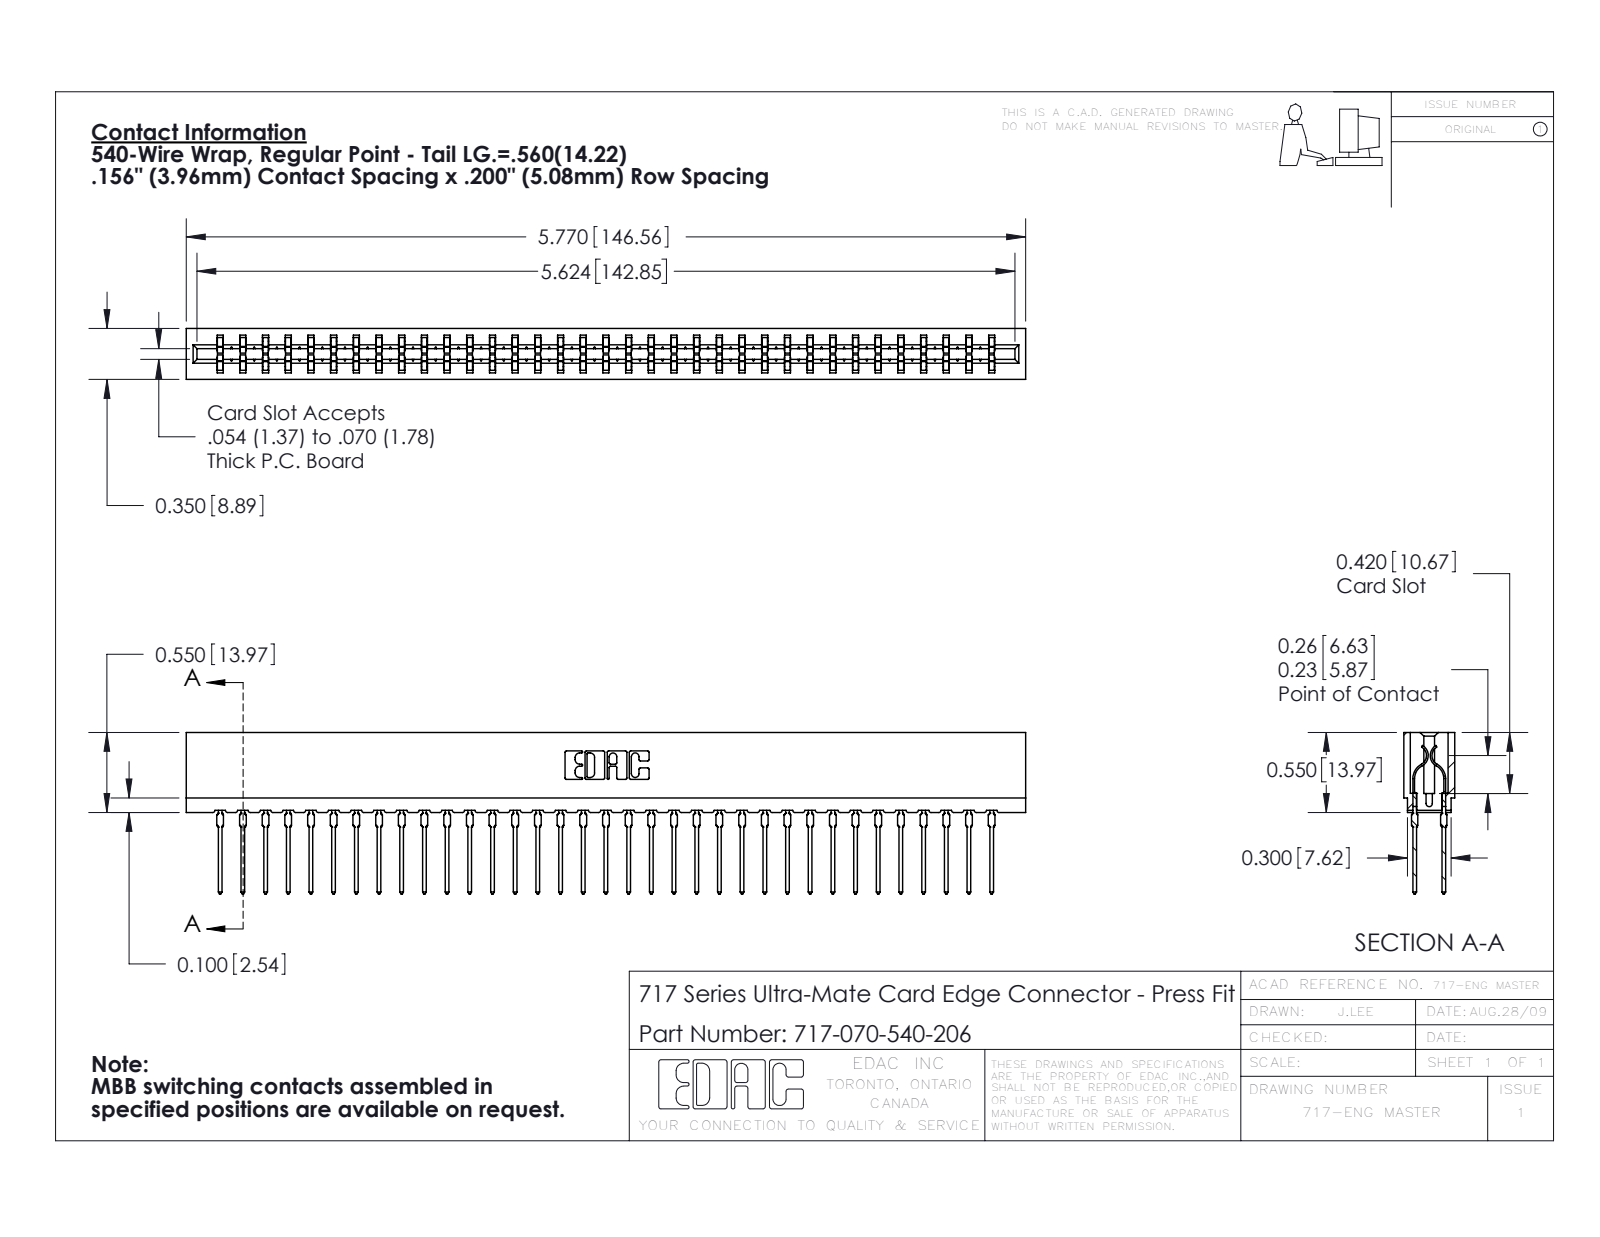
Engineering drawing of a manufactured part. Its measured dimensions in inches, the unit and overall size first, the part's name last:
Units: inches
Overall size (bounding box): 5.77 × 1.109 × 0.35
Partial cylindrical surfaces — rounded edges, fillets, slot ends (radius × count): R0.021 ×140, R0.015 ×70, R0.01 ×22, R0.005 ×8, R0.011 ×8, R0.007 ×6, R0.031 ×6, R0.026 ×3
Main face-to-face distances: 0.212, 0.138, 0.35, 0.063, 0.287, 0.076, 0.149, 0.074, 0.087, 0.263
Volume: 0.789 in³ · Surface area: 31.93 in²
Bodies: 71 solids, 6394 faces (3309 planar, 1265 cylindrical, 1820 other)
Part name (STEP PRODUCT): 717 Part_Insulator Option - 06; 717-070-540-206; 745-292-001_540
STEP written by: SolidWorks 2016 (CONFIG_CONTROL_DESIGN)
